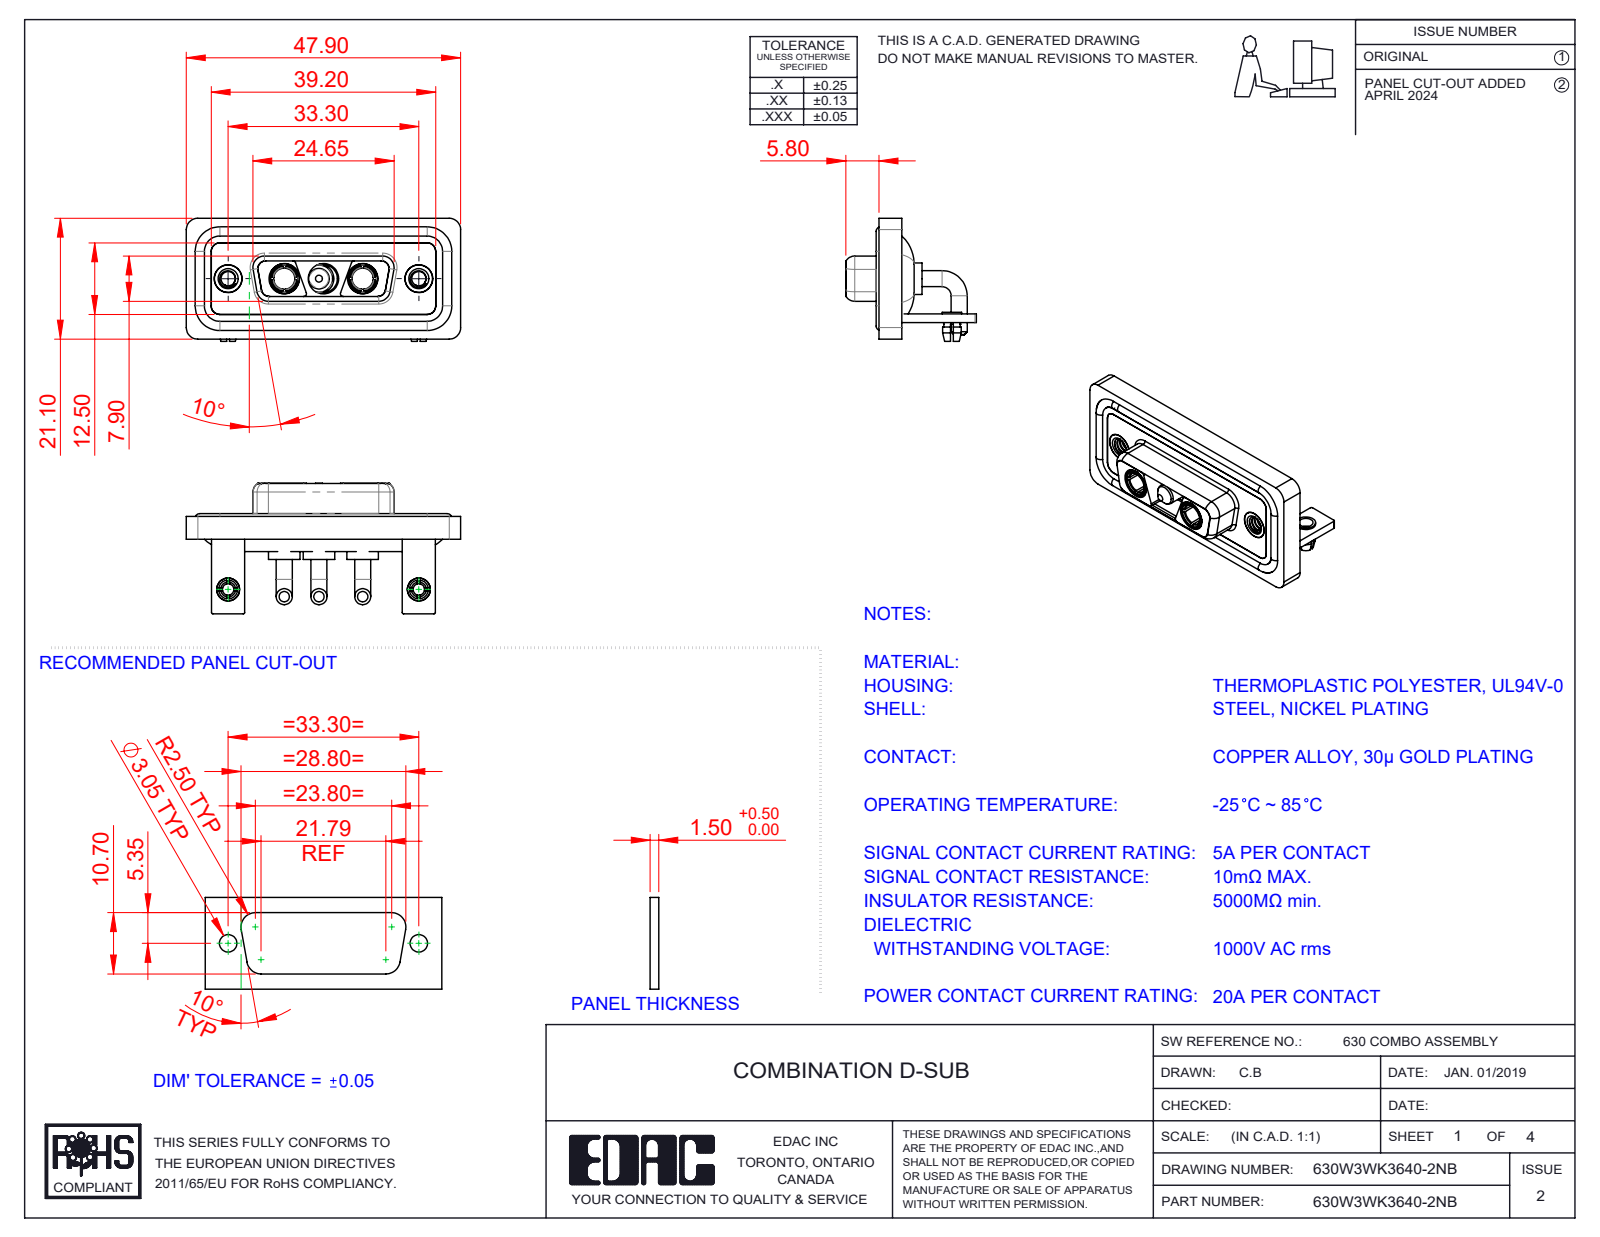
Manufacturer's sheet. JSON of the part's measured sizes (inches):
{"part_name": "630Combo Housing_3WK3; 630Combo Shell Rear_15 Contacts; 630W3WK3640-2NB; Power Pin_20A RA (+6 more)", "step_written_by": "SolidWorks 2023 (CONFIG_CONTROL_DESIGN)", "units": "inches", "bodies": {"solids": 17, "faces": 729, "planar": 246, "cylindrical": 318, "other": 165}, "overall_size": [1.886, 0.898, 0.846], "volume_in3": 0.392, "surface_area_in2": 16.56, "round_holes": [[0.191, 5], [0.098, 4], [0.209, 3], [0.079, 2], [0.126, 2], [0.146, 2], [0.157, 2], [0.159, 2], [0.197, 2]], "round_bosses_or_shafts": [[0.11, 6], [0.063, 4], [0.217, 3], [0.205, 3], [0.187, 3], [0.148, 3], [0.195, 2], [0.195, 2]], "partial_cylinders_radius": [[0.079, 21], [0.059, 18], [0.01, 16], [0.053, 12], [0.02, 9], [0.063, 8], [0.024, 4], [0.026, 4]], "face_to_face_distances": [0.016, 0.114, 0.059, 0.146, 0.071, 0.043, 0.161, 0.063, 0.098, 0.055], "hole_center_spacings": [0.27, 0.386, 0.656, 0.925, 1.311, 0.539]}
